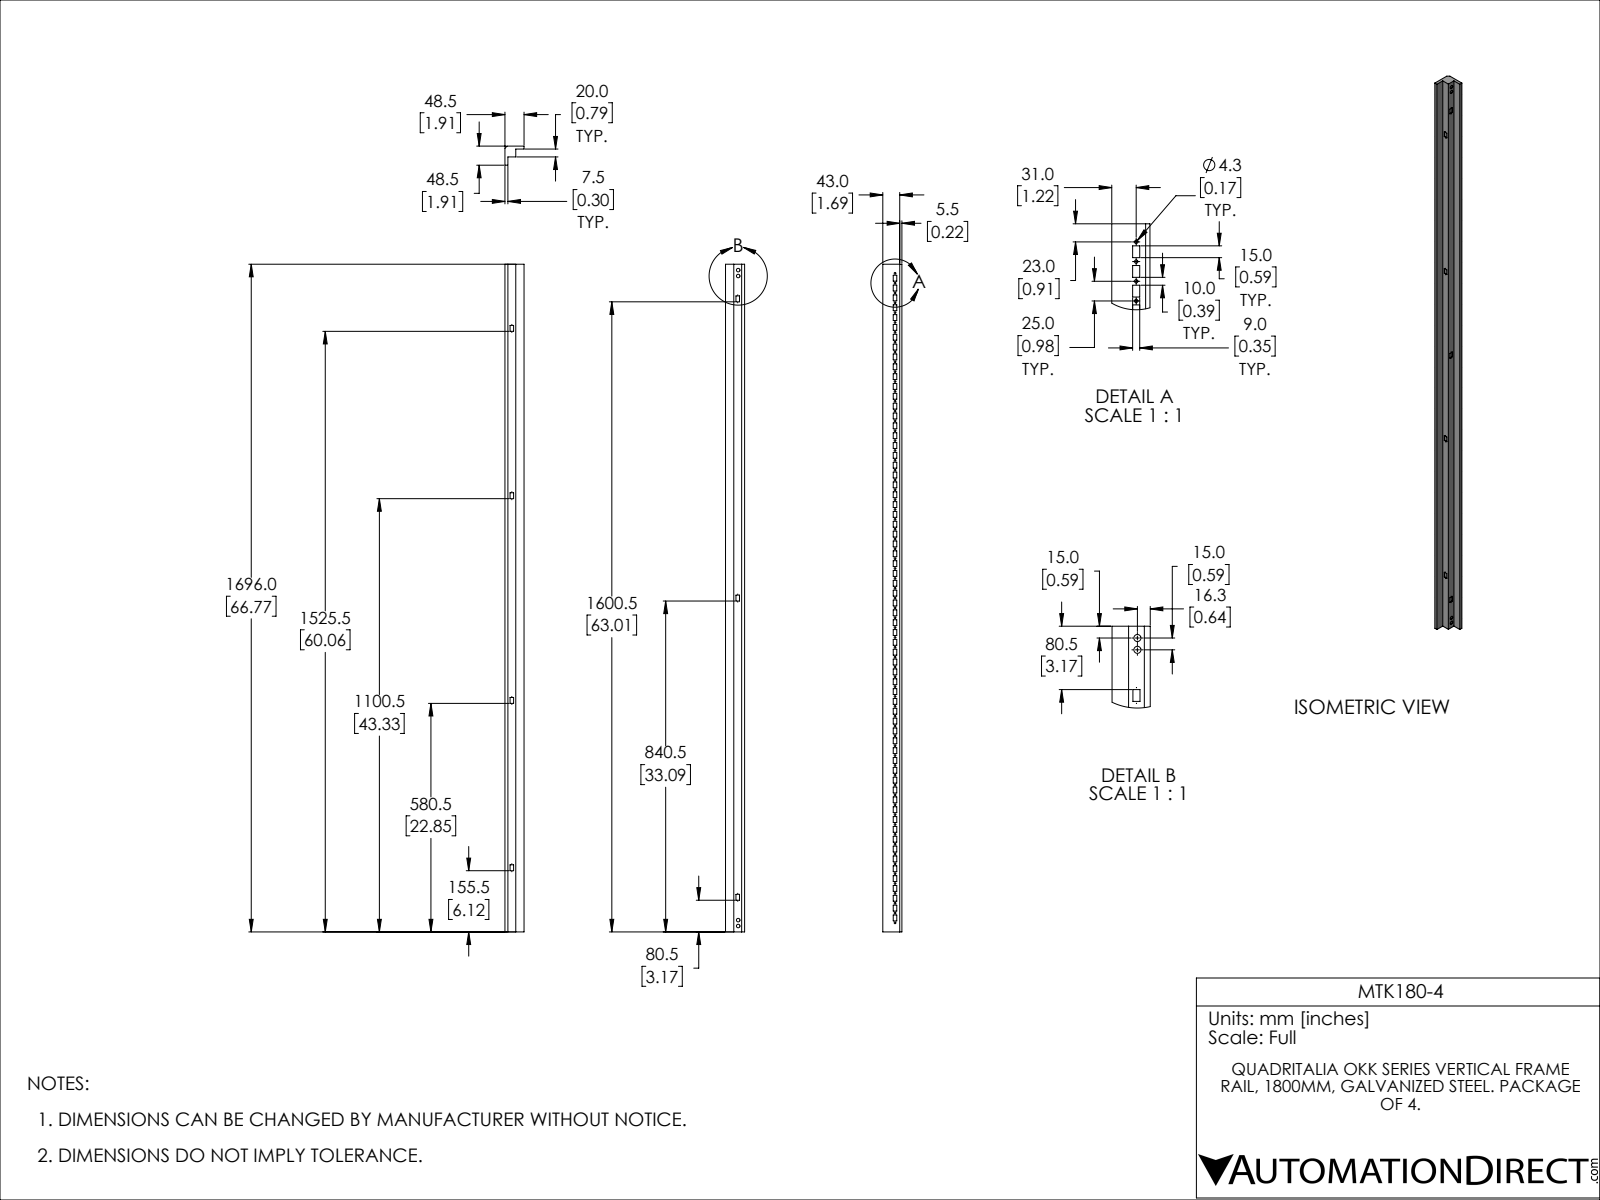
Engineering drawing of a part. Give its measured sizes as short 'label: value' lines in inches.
name: MTK180-4
written by: SolidWorks 2021 (AUTOMOTIVE_DESIGN)
unit: in
bodies: 4 solids, 4040 faces (3432 planar, 608 cylindrical, 0 other)
size: 66.772 × 9.409 × 1.909
volume: 431.1 in³; area: 2 083 in²
holes: 335× ⌀0.167, 38× ⌀0.01, 4× ⌀0.354
face distances: 2.5, 5, 0.295, 1.083, 0.787, 7.5, 2.795, 2.205, 1.909, 1.614
hole spacings: 0.984, 1.969, 2.953, 3.937, 4.921, 5.906, 6.89, 7.874
